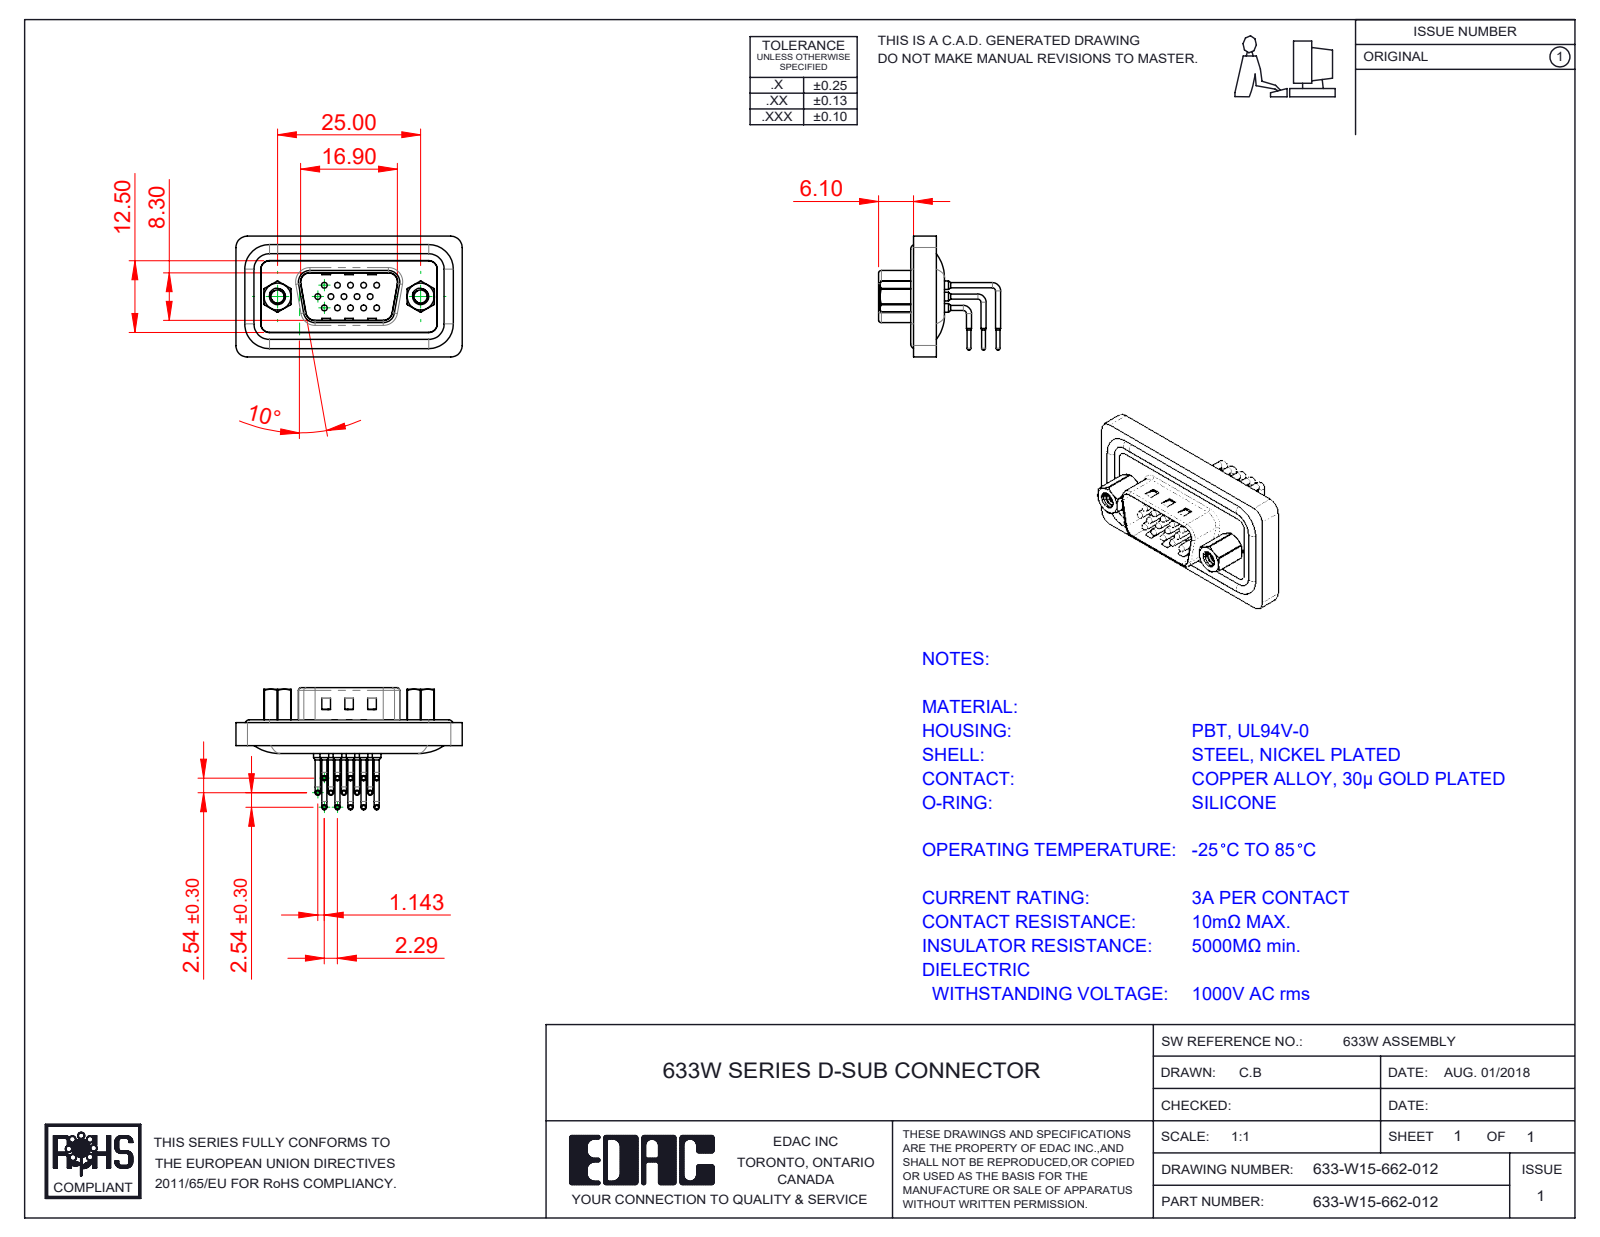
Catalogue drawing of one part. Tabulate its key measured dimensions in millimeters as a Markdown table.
| quantity | value |
| --- | --- |
| part name | 633W 4-40 Threaded Rivet_Stabilizer; 633-W15-662-012; 633W 4-40 Hex Standoff; 633W Contact Row 2 (+5 more) |
| STEP written by | SolidWorks 2016 (CONFIG_CONTROL_DESIGN) |
| units | millimeters |
| bodies | 23 solids, 2118 faces (1101 planar, 772 cylindrical, 245 other) |
| overall size | 39.51 × 21.32 × 21.1 |
| volume | 4 080 mm³ |
| surface area | 7 322 mm² |
| round holes (diameter × count) | 1 × 15, 1.5 × 15, 1.7 × 15, 2 × 15, 2.26 × 2, 2.29 × 2, 4 × 2, 4.8 × 2, 5 × 2 |
| round bosses / shafts (diameter × count) | 0.9 × 30, 0.65 × 15, 1.5 × 8, 1.6 × 4, 4.9 × 2, 2.79 × 2, 5 × 1 |
| partial cylindrical surfaces (radius × count) | 1.01 × 15, 1.5 × 14, 2 × 14, 0.5 × 8, 2.7 × 6, 0.9 × 4, 1.6 × 4, 4.3 × 4 |
| main face-to-face distances | 0.4, 2.9, 1.1, 1.6, 2.5, 4, 3.6, 1.8, 0.5, 0.7 |
| hole center spacings | 3.96, 2.28, 4.57, 2.29, 6.05, 6.04, 7.92, 6.86 |
